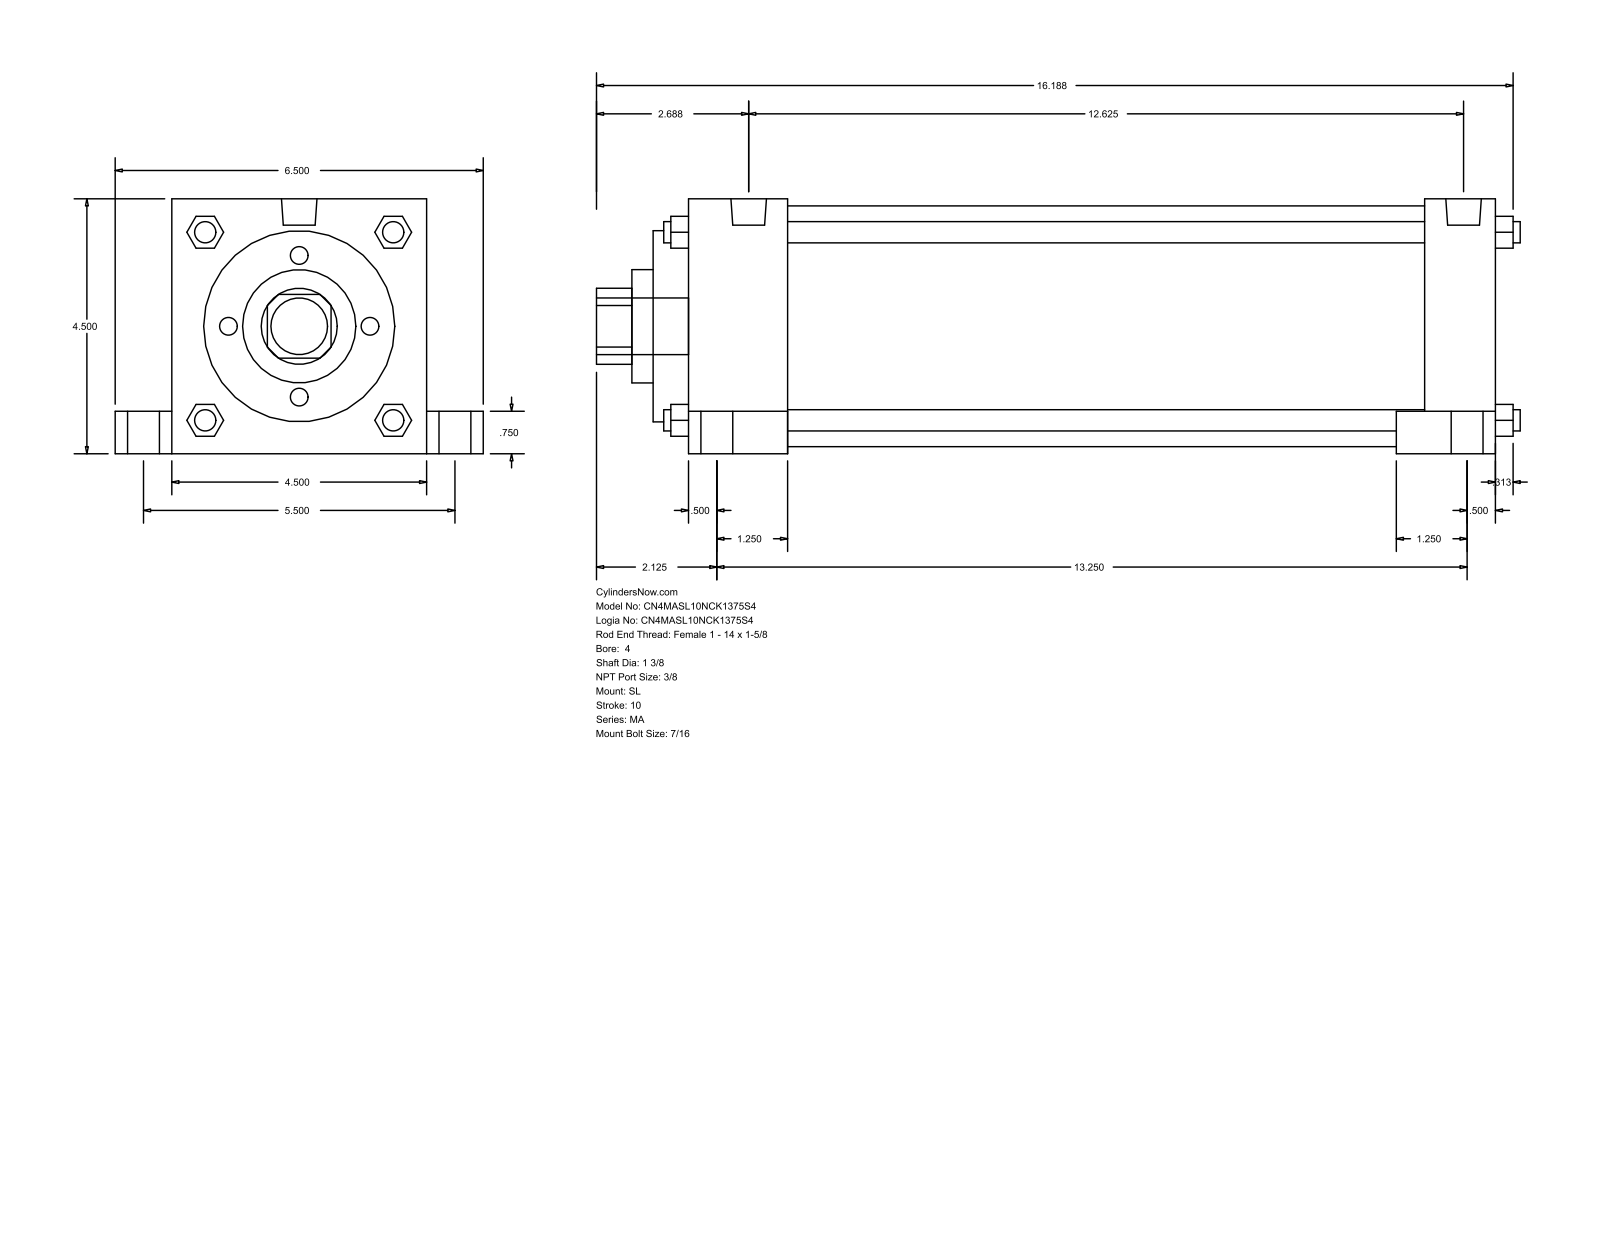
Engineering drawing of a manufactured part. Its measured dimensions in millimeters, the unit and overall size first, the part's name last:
Units: millimetres
Overall size (bounding box): 414.34 × 165.1 × 114.3
Round holes (diameter × count): ⌀34.92 ×1, ⌀50.8 ×1, ⌀85.72 ×1, ⌀107.95 ×1
Round bosses / shafts (diameter × count): ⌀20.64 ×4, ⌀14.29 ×4, ⌀11.11 ×4, ⌀9.53 ×4, ⌀15.93 ×2, ⌀25.4 ×1
Partial cylindrical surfaces — rounded edges, fillets, slot ends (radius × count): R17.06 ×1
Main face-to-face distances: 114.3, 361.96, 15.87, 377.83, 60.32, 44.45, 317.51, 346.08, 330.21, 285.76
Bodies: 0 solids, 150 faces (113 planar, 37 cylindrical, 0 other)
Part name (STEP PRODUCT): MA_SL__0400_1.375
STEP written by: GSSL Pune (CONFIG_CONTROL_DESIGN)
